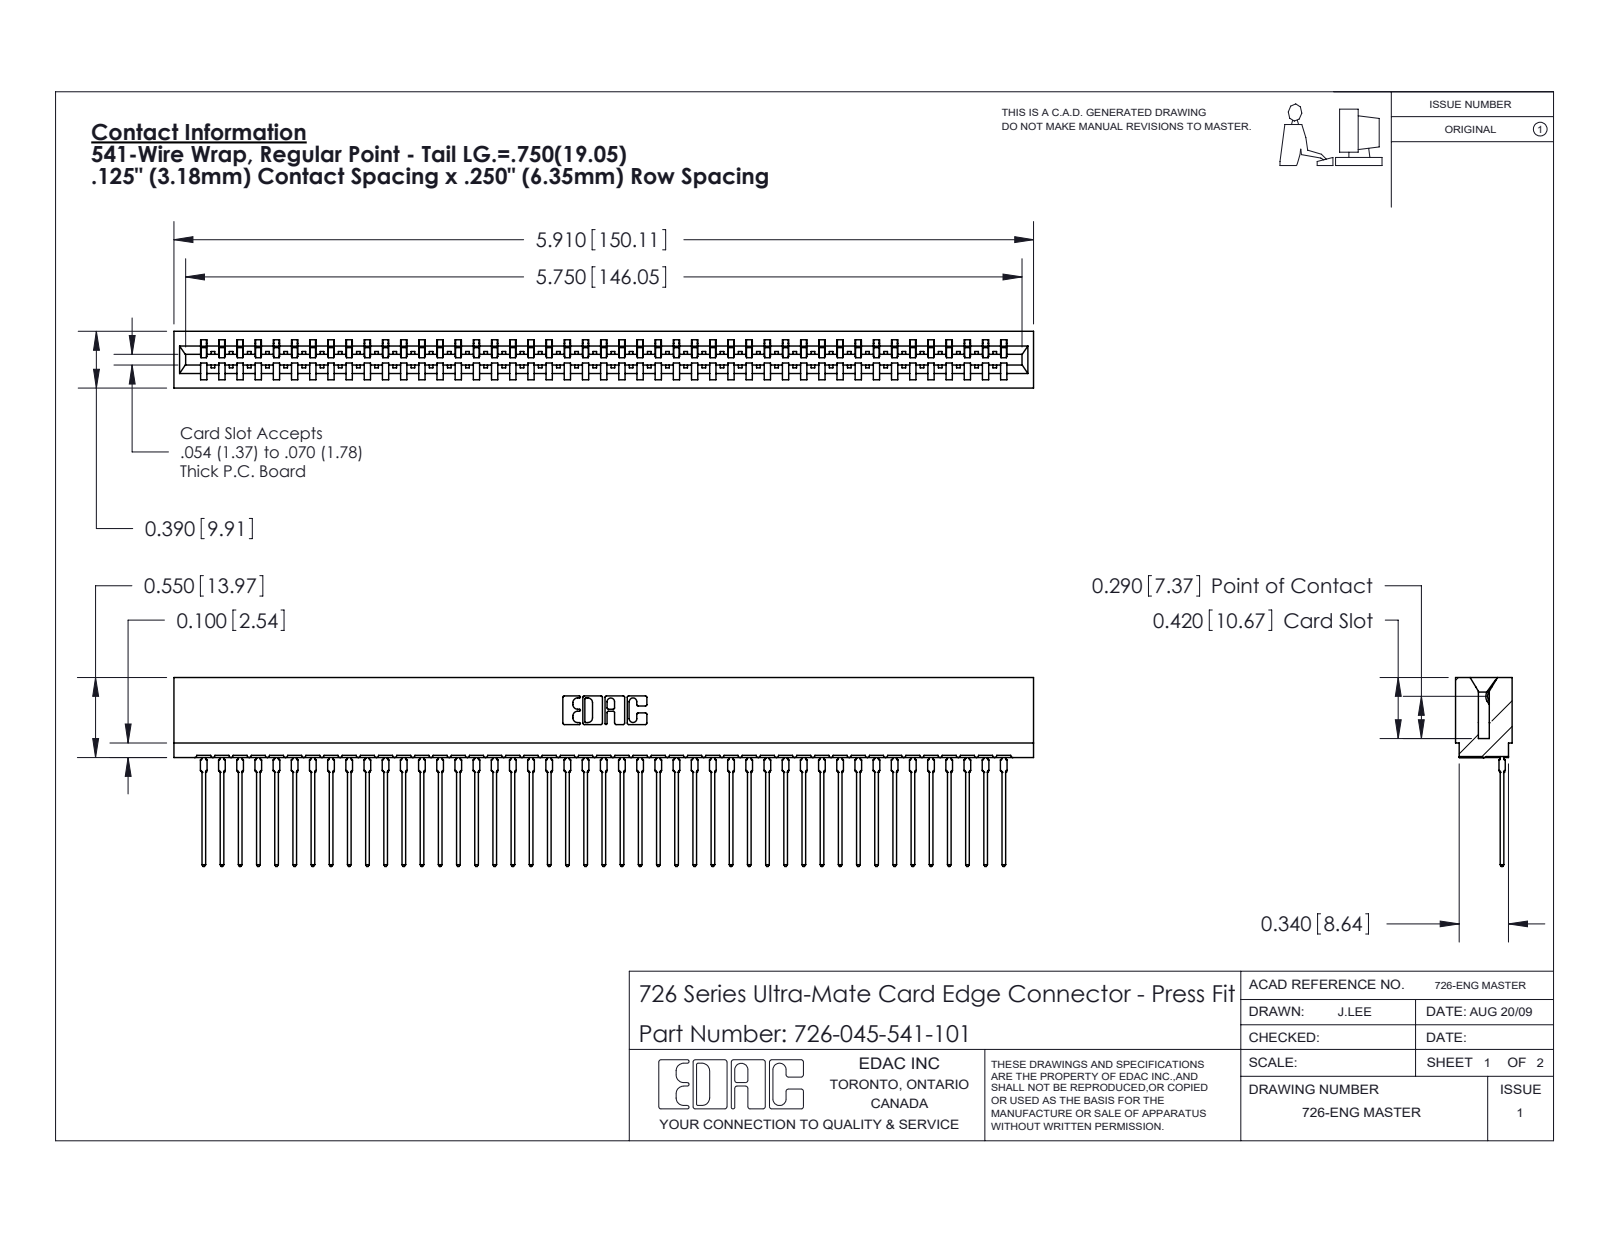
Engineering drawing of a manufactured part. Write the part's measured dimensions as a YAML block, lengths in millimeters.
part_name: "746-292-001_541; 726-045-541-101; 726 Part_.515 Slot Depth - 01"
step_written_by: "SolidWorks 2020 (CONFIG_CONTROL_DESIGN)"
units: millimeters
bodies: {solids: 46, faces: 4957, planar: 2890, cylindrical: 897, other: 1170}
overall_size: [150.1, 33, 9.9]
volume: 13600
surface_area: 21880
partial_cylinders:
  - {radius: 0.5, count: 90}
  - {radius: 0.4, count: 46}
  - {radius: 0.3, count: 22}
  - {radius: 0.2, count: 6}
  - {radius: 0.8, count: 6}
  - {radius: 0.1, count: 4}
  - {radius: 0.3, count: 4}
  - {radius: 0.7, count: 3}
face_to_face_distances: [1.4, 8.5, 9.9, 0.6, 7.8, 6.4, 2.1, 7, 9.3, 0.8]
